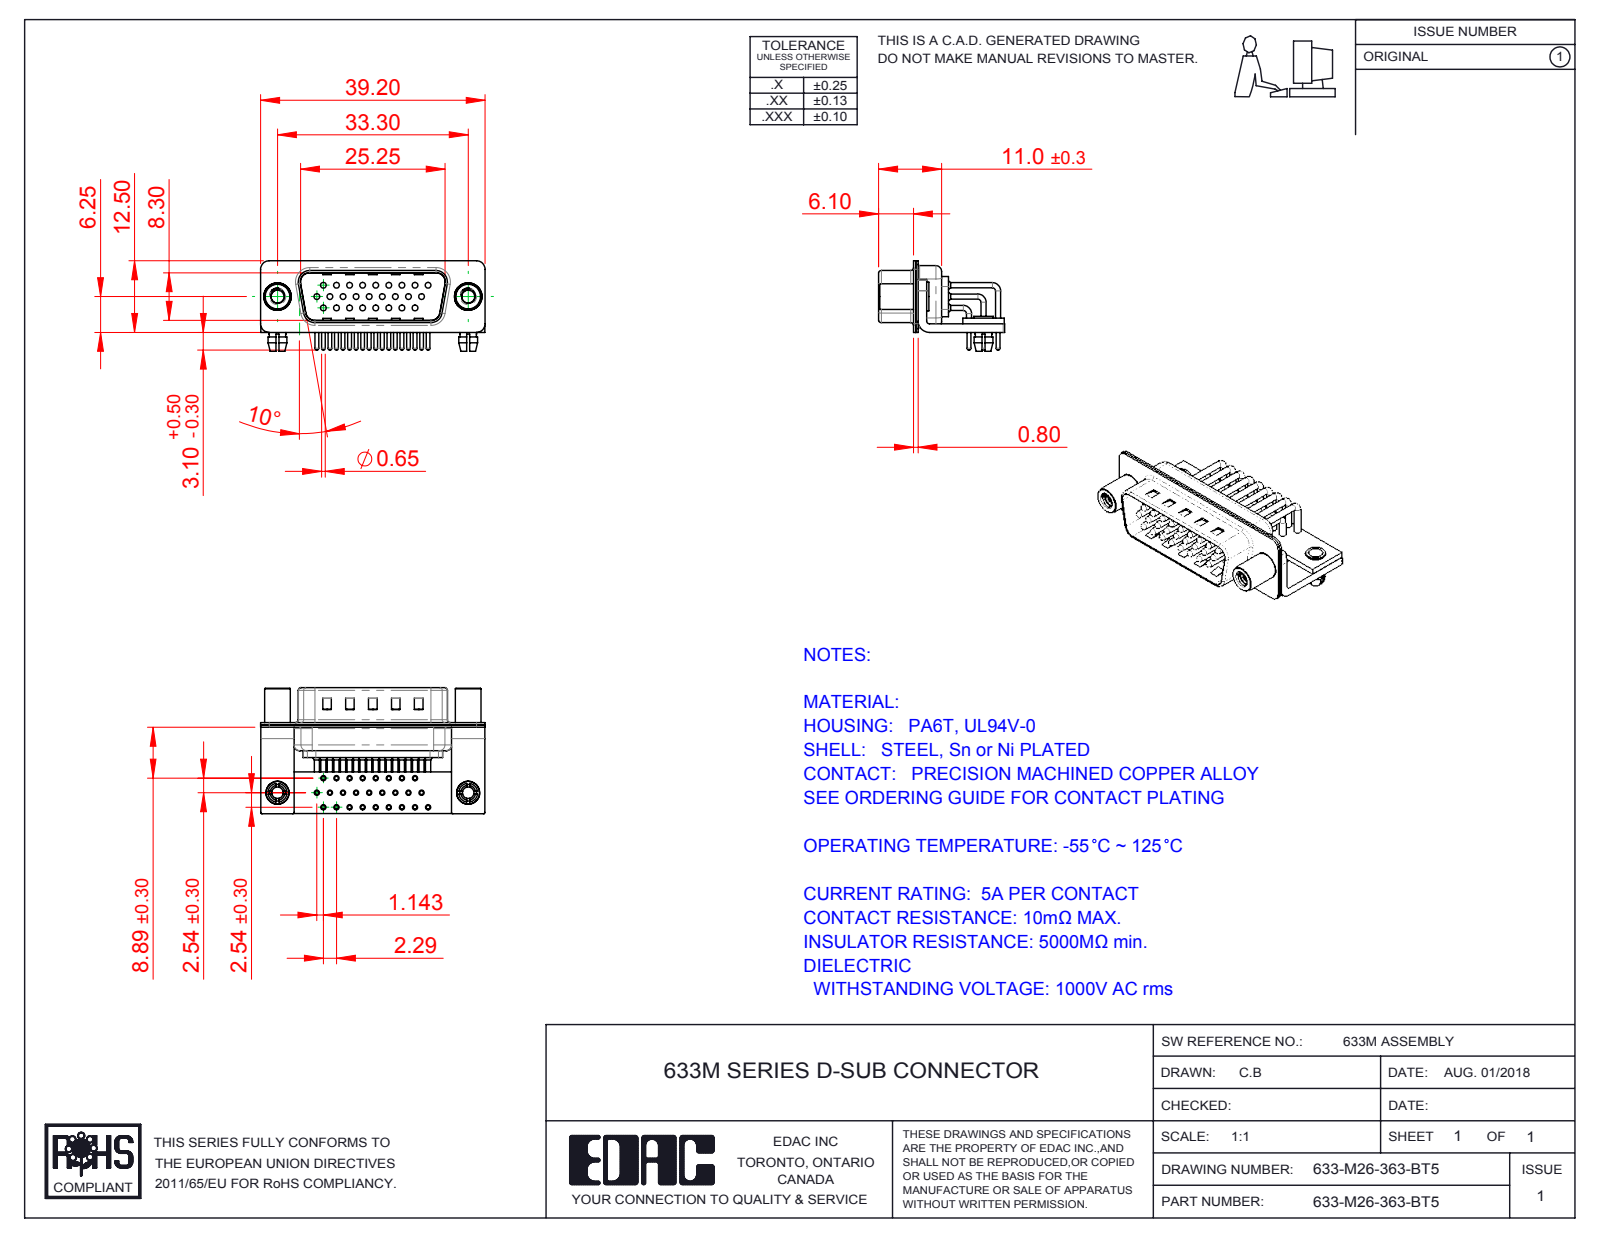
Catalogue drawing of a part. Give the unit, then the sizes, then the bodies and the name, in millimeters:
Units: millimetres
Overall size (bounding box): 39.2 × 22 × 15.8
Round holes (diameter × count): ⌀2 ×28, ⌀0.9 ×26, ⌀1 ×26, ⌀1.7 ×26, ⌀2.26 ×2, ⌀2.5 ×2, ⌀3.2 ×2, ⌀4 ×2, ⌀4.8 ×2
Round bosses / shafts (diameter × count): ⌀1.5 ×26, ⌀0.9 ×26, ⌀0.65 ×26, ⌀5 ×2, ⌀4.9 ×2, ⌀4.5 ×2, ⌀4 ×2, ⌀3.4 ×2
Partial cylindrical surfaces — rounded edges, fillets, slot ends (radius × count): R1.01 ×26, R0.25 ×16, R1.5 ×16, R2 ×13, R0.5 ×9, R1.6 ×8, R0.6 ×4, R0.65 ×4
Main face-to-face distances: 0.4, 1.5, 0.85, 0.8, 1, 1.25, 1.9, 10.4, 9.55, 2.5
Hole centre spacings: 4.57, 2.29, 2.28, 3.96, 6.86, 4.27, 6.05, 2.78
Volume: 2 794 mm³ · Surface area: 8 558 mm²
Bodies: 36 solids, 3444 faces (1879 planar, 1217 cylindrical, 348 other)
Part name (STEP PRODUCT): 633M Shell Front_26 Contacts; 633M Contact Row 2; 633M Contact Row 1; 633M 4-40 Threaded Standoff (+7 more)
STEP written by: SolidWorks 2016 (CONFIG_CONTROL_DESIGN)
